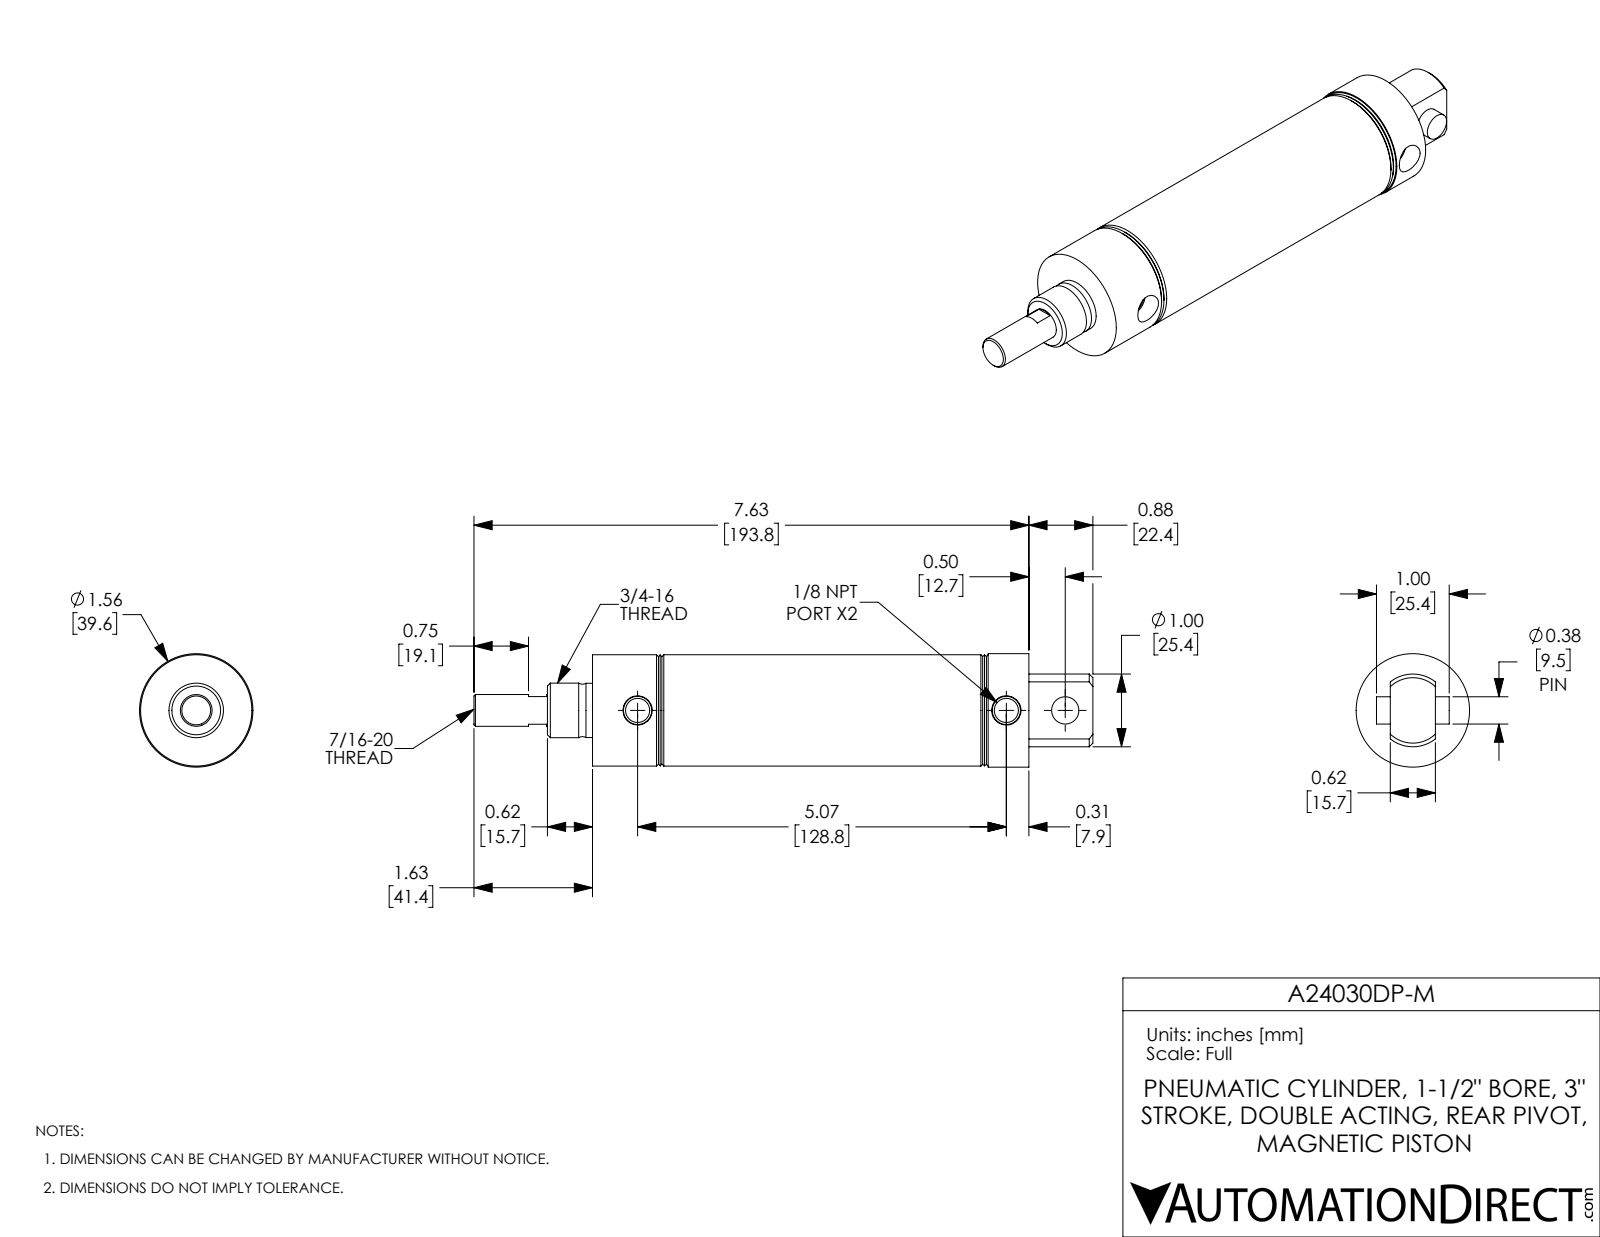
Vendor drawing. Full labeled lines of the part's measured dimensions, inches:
Part name (STEP PRODUCT): A24030DP-M-MainBody; A24030DP-M-Rod; A24030DP-M-Pin; A24030DP-M
STEP written by: SolidWorks 2017 (AUTOMOTIVE_DESIGN)
Units: inches
Bodies: 3 solids, 84 faces (22 planar, 28 cylindrical, 34 other)
Overall size (bounding box): 8.51 × 1.56 × 1.56
Volume: 7.073 in³ · Surface area: 76.16 in²
Round holes (diameter × count): ⌀0.332 ×2, ⌀0.375 ×1, ⌀0.437 ×1, ⌀1.5 ×1
Round bosses / shafts (diameter × count): ⌀1.56 ×1, ⌀1.53 ×1, ⌀0.75 ×1, ⌀0.746 ×1
Partial cylindrical surfaces — rounded edges, fillets, slot ends (radius × count): R0.5 ×1
Main face-to-face distances: 1.25, 4.75, 3.5, 0.5, 3, 4.25, 1.75, 6, 0.62, 0.88
Hole centre spacings: 0.81, 5.07, 5.88
